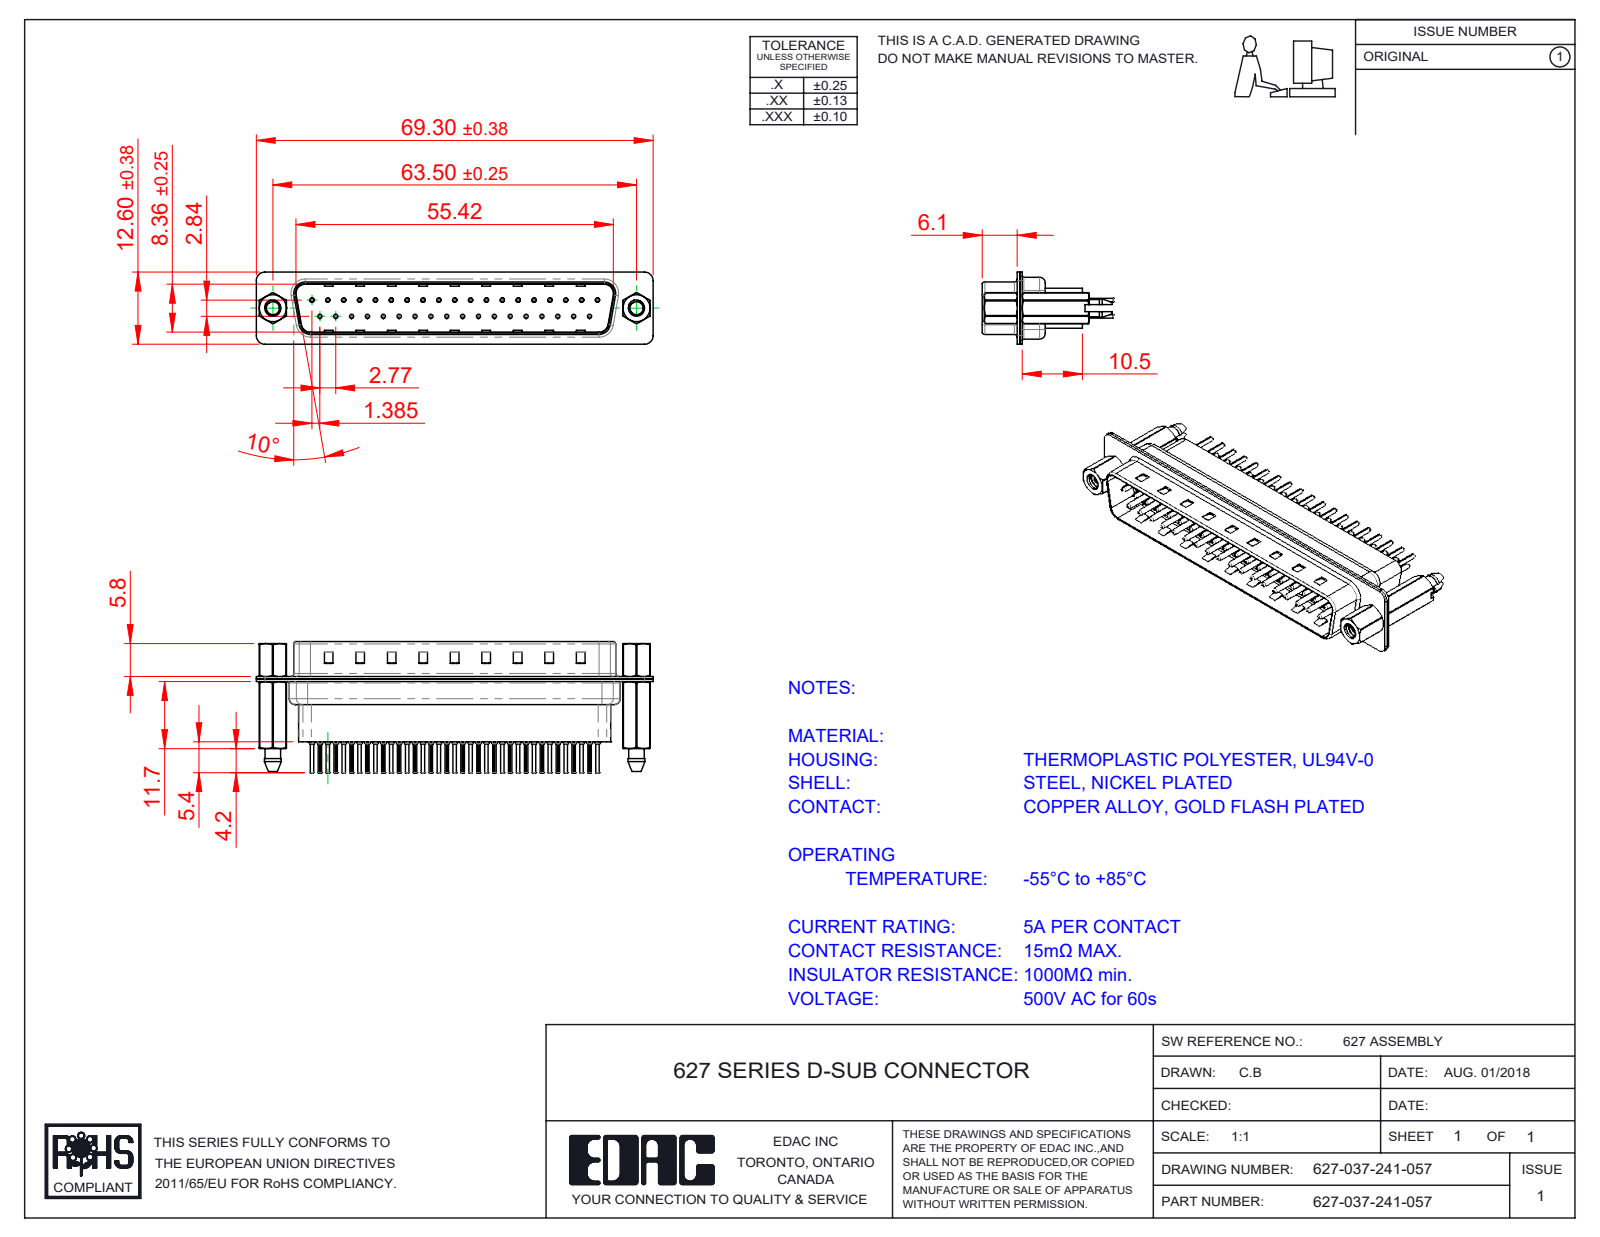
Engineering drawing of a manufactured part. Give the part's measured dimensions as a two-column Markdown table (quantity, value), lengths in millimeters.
| quantity | value |
| --- | --- |
| part name | 627 4-40 Threaded Boardlock_HP41; 627 4-40 Hex Standoff; 627 Housing_37 HP; 627 Shell Rear_37 Contacts (+4 more) |
| STEP written by | SolidWorks 2020 (CONFIG_CONTROL_DESIGN) |
| units | millimeters |
| bodies | 44 solids, 4272 faces (1145 planar, 1648 cylindrical, 1479 other) |
| overall size | 69.3 × 22.8 × 12.6 |
| volume | 5 817 mm³ |
| surface area | 14 880 mm² |
| round holes (diameter × count) | 0.2 × 37, 0.35 × 37, 1.1 × 37, 1.6 × 37, 2.26 × 2, 2.29 × 2, 4 × 2, 4.8 × 2 |
| round bosses / shafts (diameter × count) | 2 × 37, 1.5 × 37, 0.75 × 37, 0.6 × 37, 4.9 × 2, 2.79 × 2 |
| partial cylindrical surfaces (radius × count) | 0.1 × 74, 1.5 × 18, 2 × 12, 1.6 × 10, 0.5 × 8, 0.25 × 4, 0.6 × 4, 0.65 × 4 |
| main face-to-face distances | 0.4, 0.82, 9.58, 0.45, 0.68, 7.68, 1.5, 1.08, 8.08, 8.76 |
| hole center spacings | 3.16, 2.77, 5.54, 8.31, 5.04, 10.1, 11.08, 12.78 |
